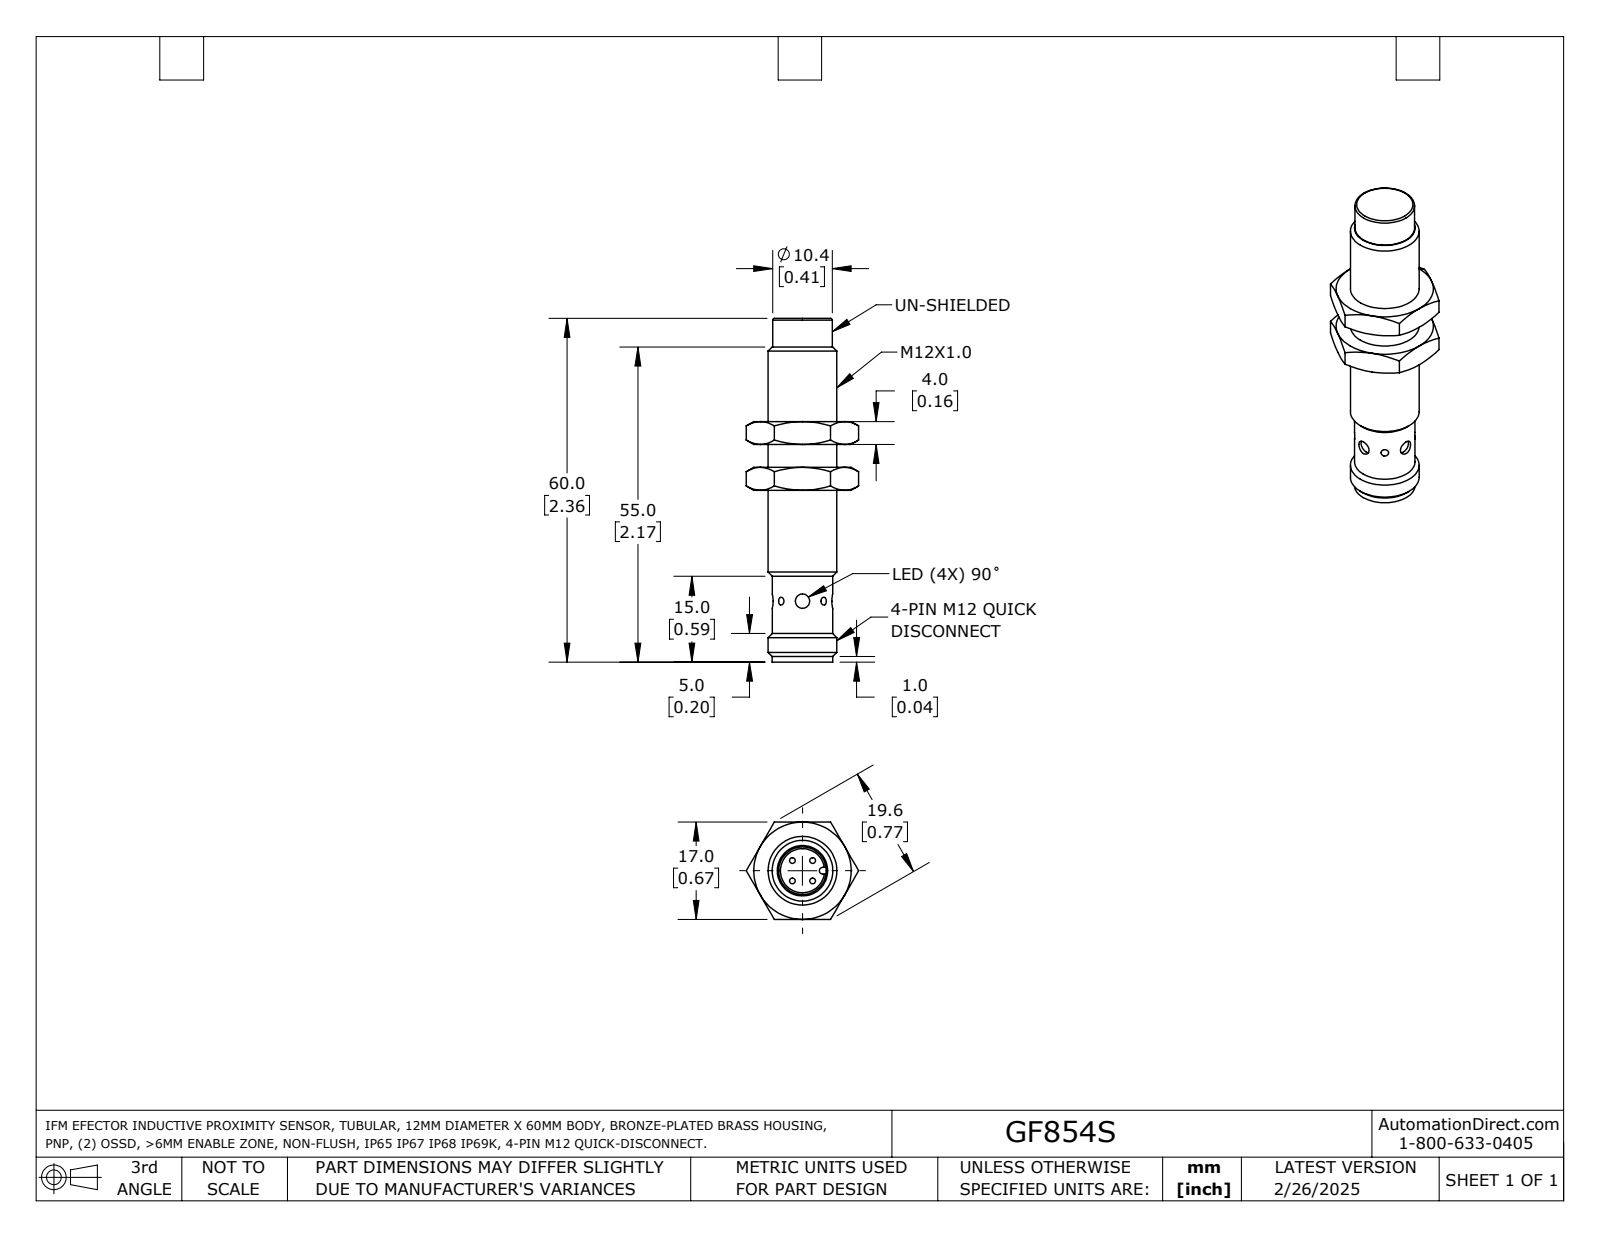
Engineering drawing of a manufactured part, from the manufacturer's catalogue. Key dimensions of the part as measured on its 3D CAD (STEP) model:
Part name (STEP PRODUCT): GF854S
STEP written by: SolidWorks 2024 (AUTOMOTIVE_DESIGN)
Units: millimetres
Bodies: 3 solids, 119 faces (23 planar, 25 cylindrical, 71 other)
Overall size (bounding box): 60 × 19.63 × 17
Volume: 7 049 mm³ · Surface area: 3 941 mm²
Round holes (diameter × count): ⌀2.5 ×2, ⌀8.3 ×1, ⌀10.92 ×1
Round bosses / shafts (diameter × count): ⌀12 ×1, ⌀10.6 ×1, ⌀10.55 ×1, ⌀10.4 ×1
Partial cylindrical surfaces — rounded edges, fillets, slot ends (radius × count): R0.6 ×1
Main face-to-face distances: 4, 8, 17, 12, 30, 18, 22, 26, 51.1, 33.1
